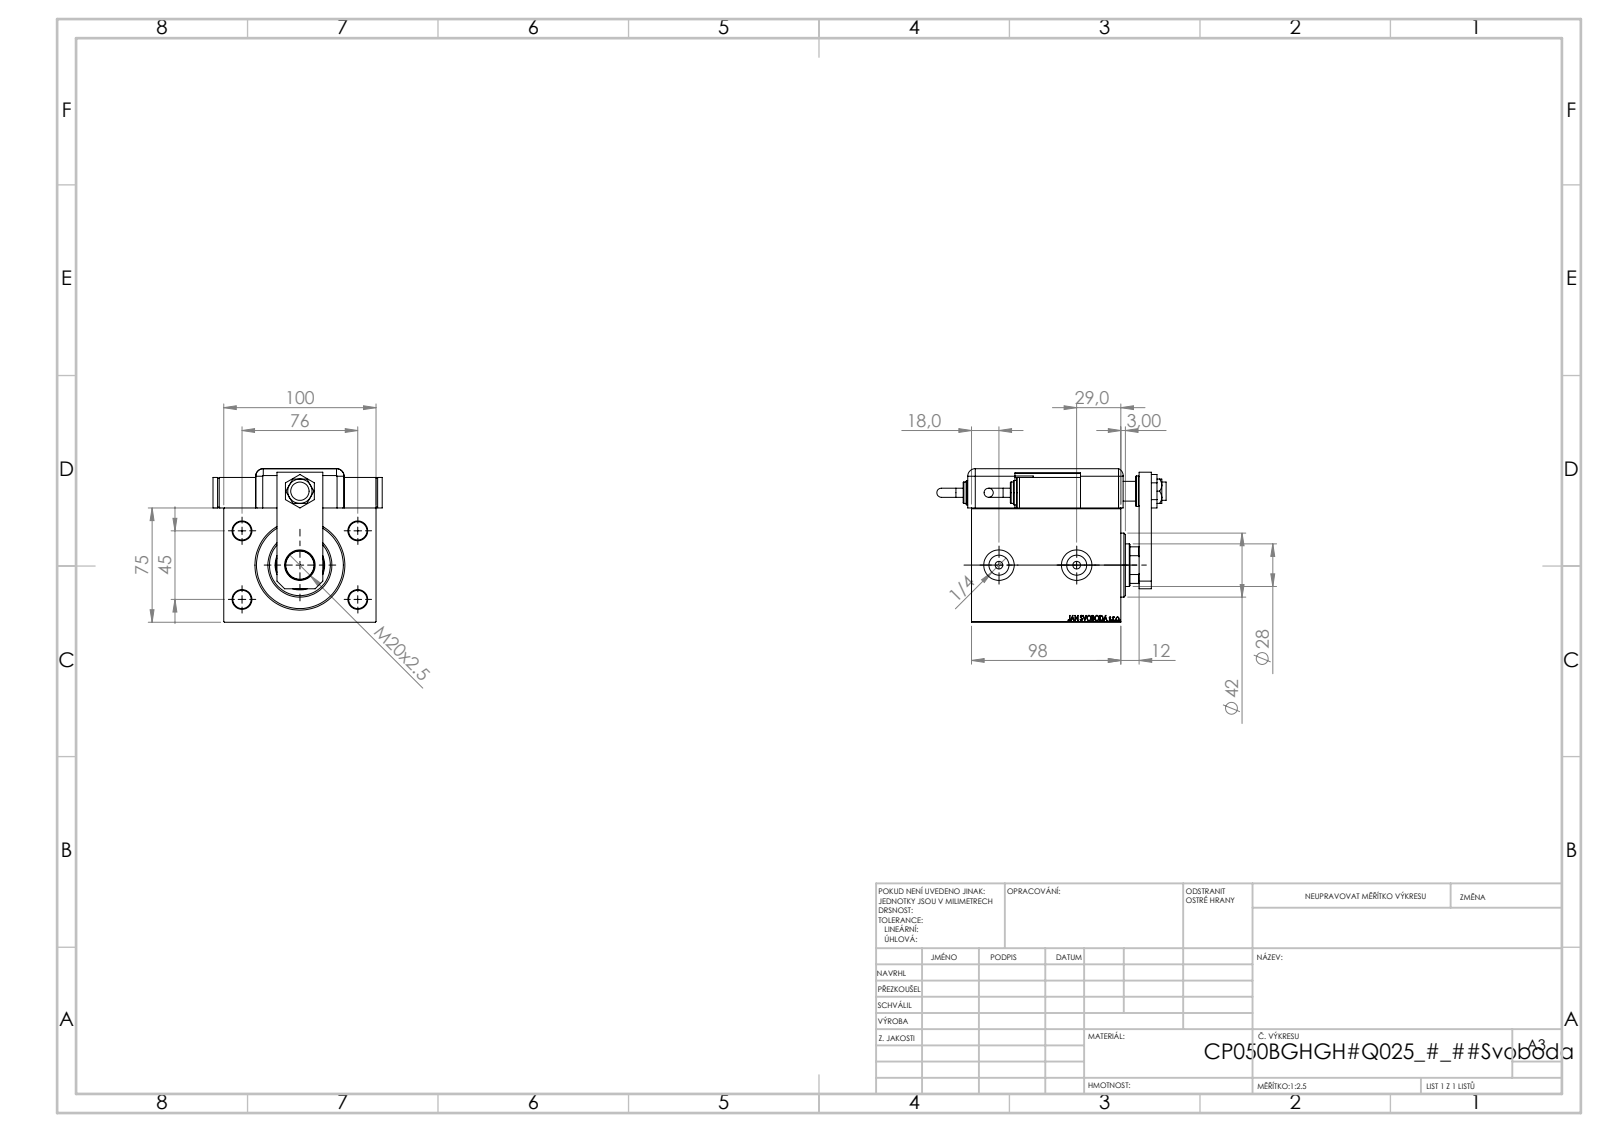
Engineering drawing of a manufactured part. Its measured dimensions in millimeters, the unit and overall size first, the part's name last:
Units: millimetres
Overall size (bounding box): 150.46 × 111 × 100.8
Round holes (diameter × count): ⌀12 ×5, ⌀20 ×3, ⌀4 ×2, ⌀5 ×2, ⌀8 ×2, ⌀13.16 ×2, ⌀13 ×1, ⌀14 ×1, ⌀18.5 ×1, ⌀28 ×1, ⌀31.5 ×1, ⌀32.5 ×1
Round bosses / shafts (diameter × count): ⌀20 ×3, ⌀16 ×2, ⌀14 ×2, ⌀6 ×2, ⌀42 ×1
Partial cylindrical surfaces — rounded edges, fillets, slot ends (radius × count): R5 ×9, R10 ×1, R13.5 ×1
Main face-to-face distances: 75, 3, 98, 100, 14, 20, 84, 25.8, 100.8, 13.5
Hole centre spacings: 44.16, 45, 46.04, 76, 80.53, 88.32, 20, 48.5
Volume: 821 065 mm³ · Surface area: 148 913 mm²
Bodies: 13 solids, 1268 faces (608 planar, 111 cylindrical, 549 other)
Part name (STEP PRODUCT): ZARAZKA_Q; SWITCH_Q_FRONT_BACK; V450CM_B_VCP; SWITCH DIM A_G (+7 more)
STEP written by: SolidWorks 2019 (CONFIG_CONTROL_DESIGN)
